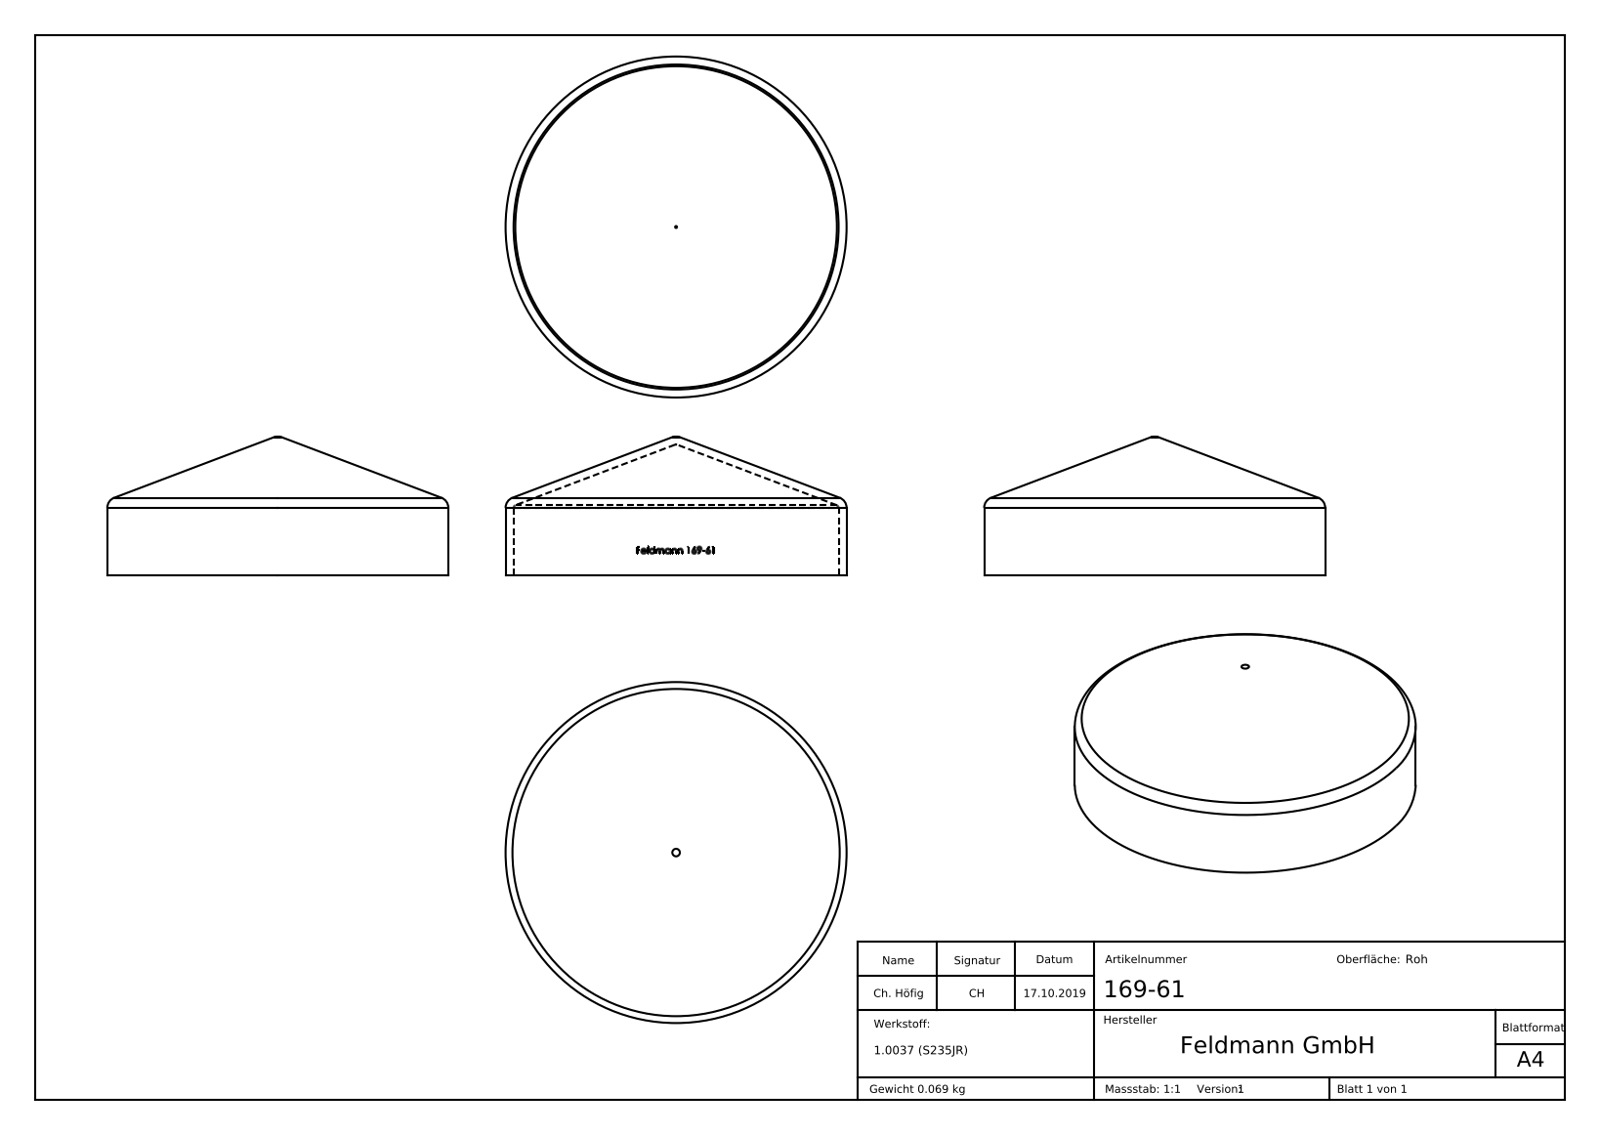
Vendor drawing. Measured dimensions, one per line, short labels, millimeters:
name: 169-61
written by: SolidWorks 2015 (CONFIG_CONTROL_DESIGN)
unit: mm
bodies: 1 solid, 183 faces (80 planar, 22 cylindrical, 81 other)
size: 64 × 64 × 26
volume: 8 832 mm³; area: 12 084 mm²
holes: 1× ⌀61
bosses: 1× ⌀64
rounds: 1× R30.6
face distances: 7.75, 0.39, 4.68, 2.02, 1.32, 1.26, 1.65, 2.97, 2.96, 6.64
